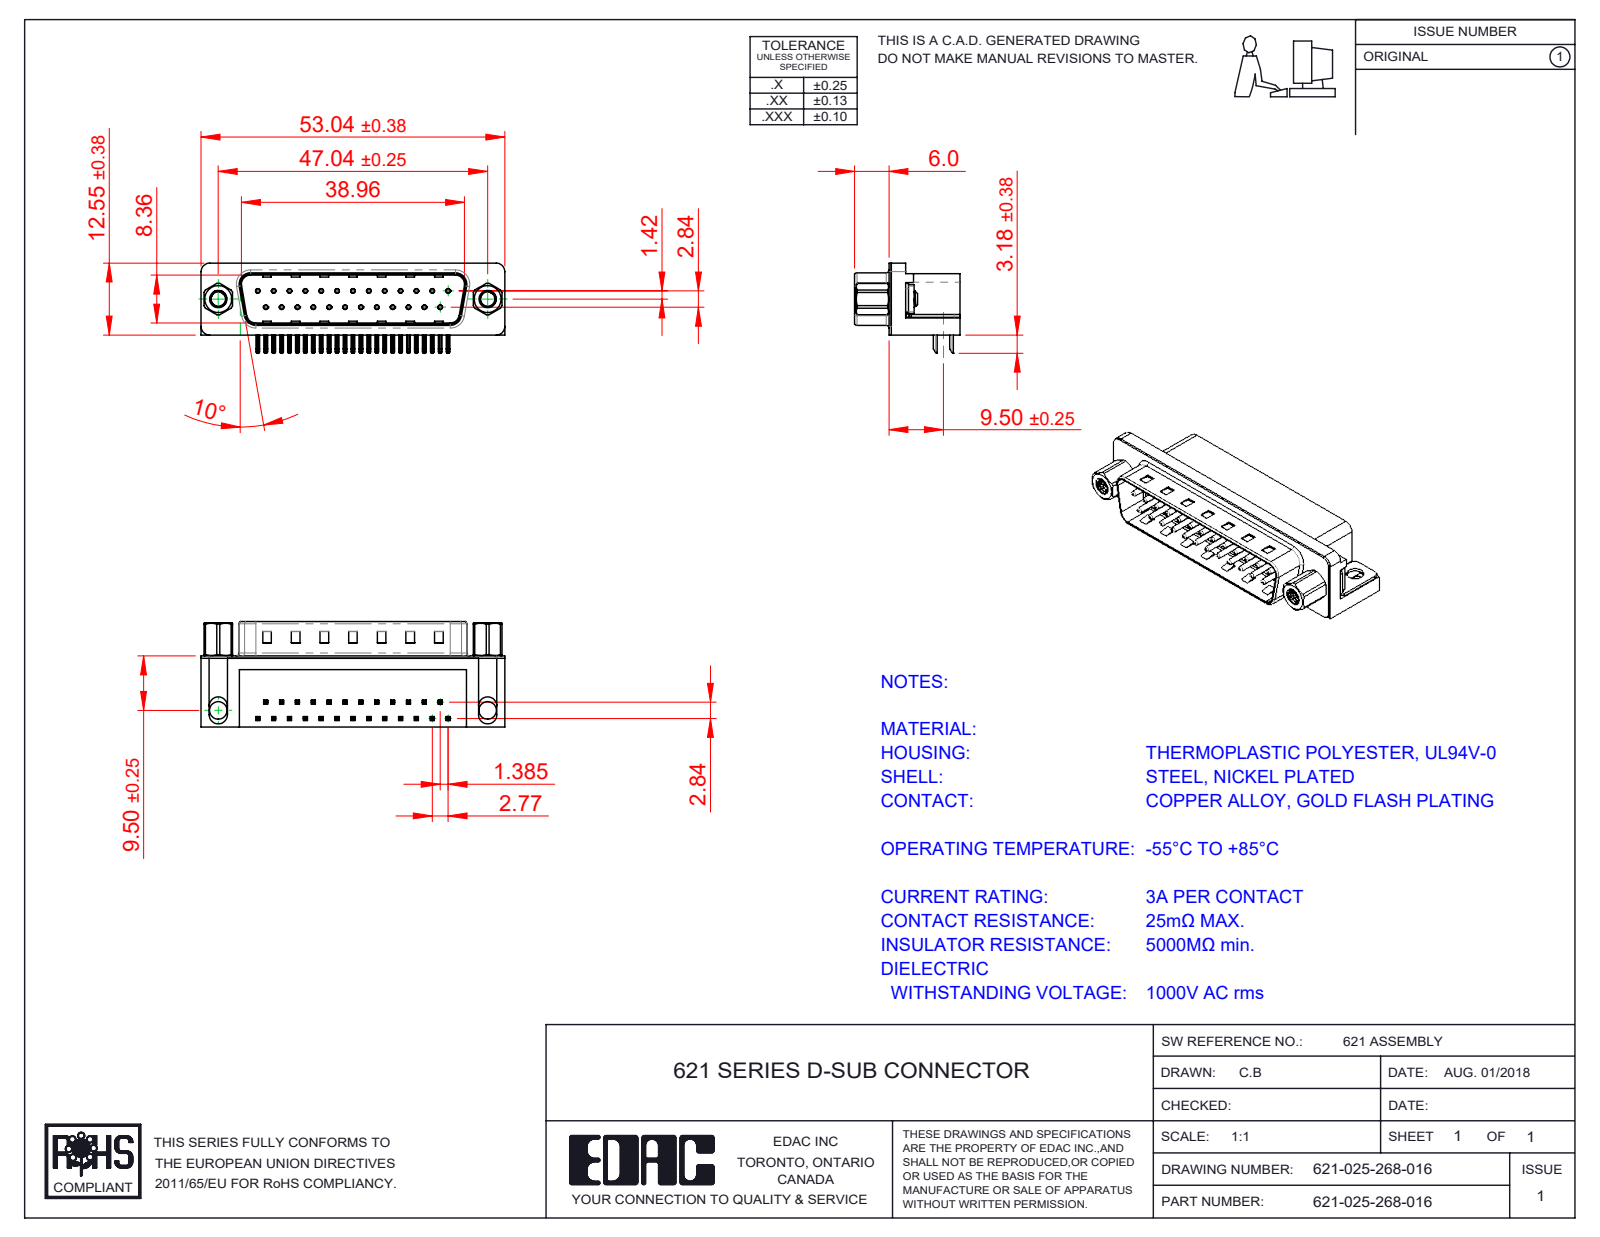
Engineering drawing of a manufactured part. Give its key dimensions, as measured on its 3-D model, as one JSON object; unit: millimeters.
{"part_name": "621 Shell_25 Socket; 621 Housing_25 Socket; 621 M3 Threaded Rivet; 621 Contact Top (+4 more)", "step_written_by": "SolidWorks 2016 (CONFIG_CONTROL_DESIGN)", "units": "millimeters", "bodies": {"solids": 33, "faces": 2409, "planar": 1425, "cylindrical": 755, "other": 229}, "overall_size": [53.04, 18.4, 15.73], "volume_mm3": 6585, "surface_area_mm2": 8202, "round_holes": [[0.35, 25], [0.8, 25], [2.5, 2], [3.05, 2], [4, 2], [4.8, 2], [5, 2]], "round_bosses_or_shafts": [[0.75, 25], [4.9, 2], [4.75, 2], [3.9, 2], [3, 2]], "partial_cylinders_radius": [[0.25, 108], [0.12, 50], [1, 16], [0.5, 9], [1.6, 8], [1.5, 7], [0.9, 4], [2, 4]], "face_to_face_distances": [0.4, 12, 10.35, 2.1, 8.76, 10.46, 1.7, 10.86, 12.4, 9], "hole_center_spacings": [3.16, 2.77, 5.54, 8.31, 11.08, 13.85, 16.62, 5.03]}
